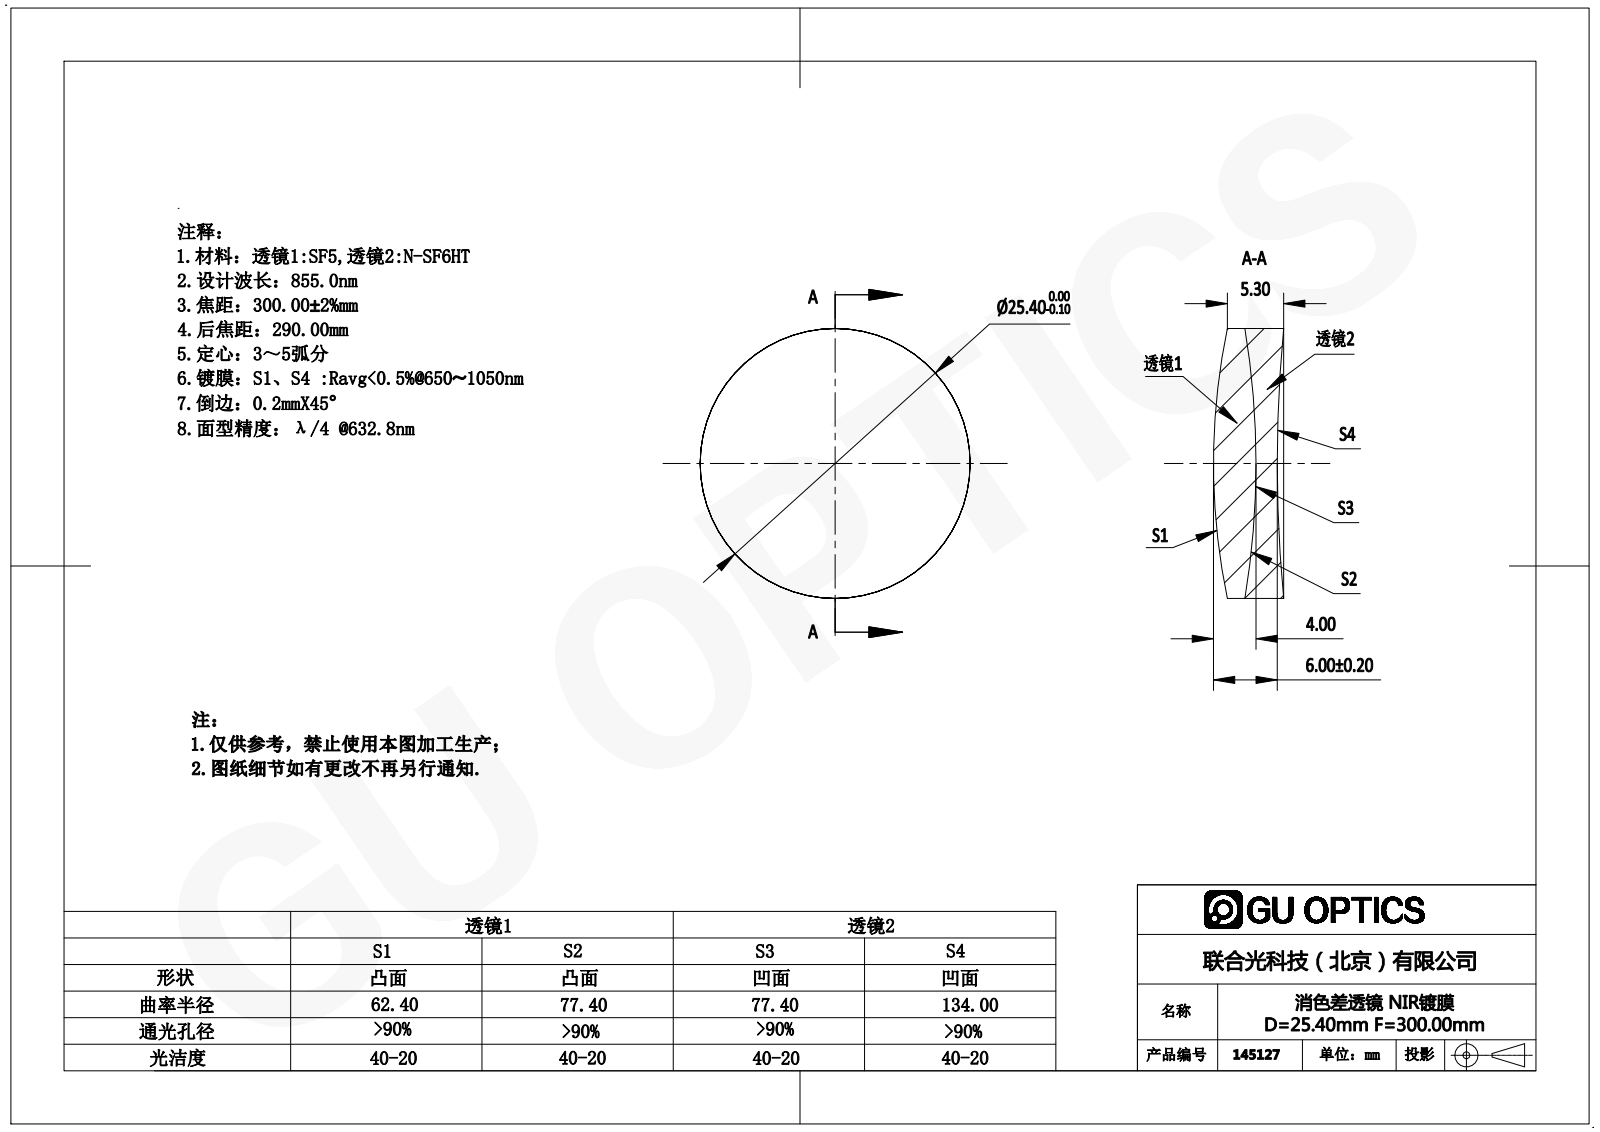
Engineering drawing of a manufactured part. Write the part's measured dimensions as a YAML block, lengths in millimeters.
part_name: "145127"
step_written_by: "SolidWorks 2016 (AUTOMOTIVE_DESIGN)"
units: millimeters
bodies: {solids: 2, faces: 12, planar: 0, cylindrical: 4, other: 8}
overall_size: [25.4, 25.4, 6.6]
volume: 2863
surface_area: 2463
round_bosses_or_shafts:
  - {diameter: 25.4, count: 1}
